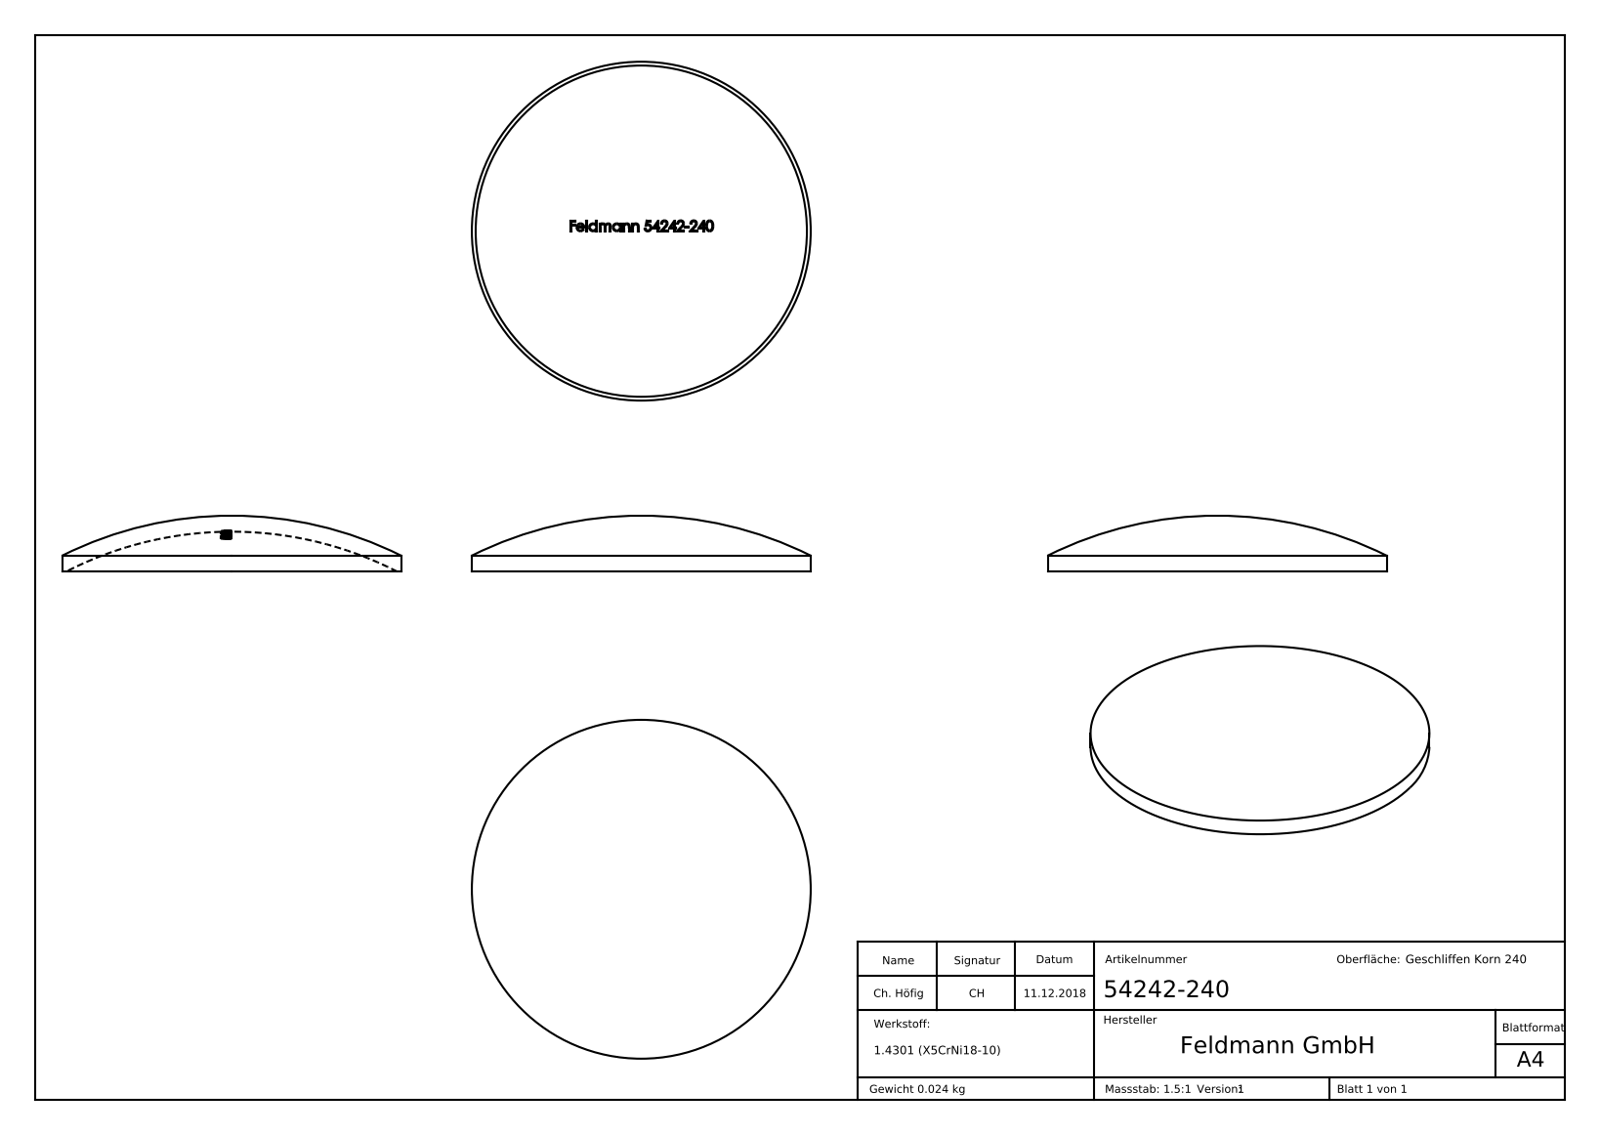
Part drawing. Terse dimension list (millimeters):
name: 54242-240
written by: SolidWorks 2015 (CONFIG_CONTROL_DESIGN)
unit: mm
bodies: 1 solid, 246 faces (122 planar, 2 cylindrical, 122 other)
size: 42.4 × 42.4 × 7
volume: 2 980 mm³; area: 3 257 mm²
bosses: 1× ⌀42.4
face distances: 0.44, 3.66, 0.39, 12.97, 2.97, 0.31, 4.7, 1.19, 13.09, 0.88
